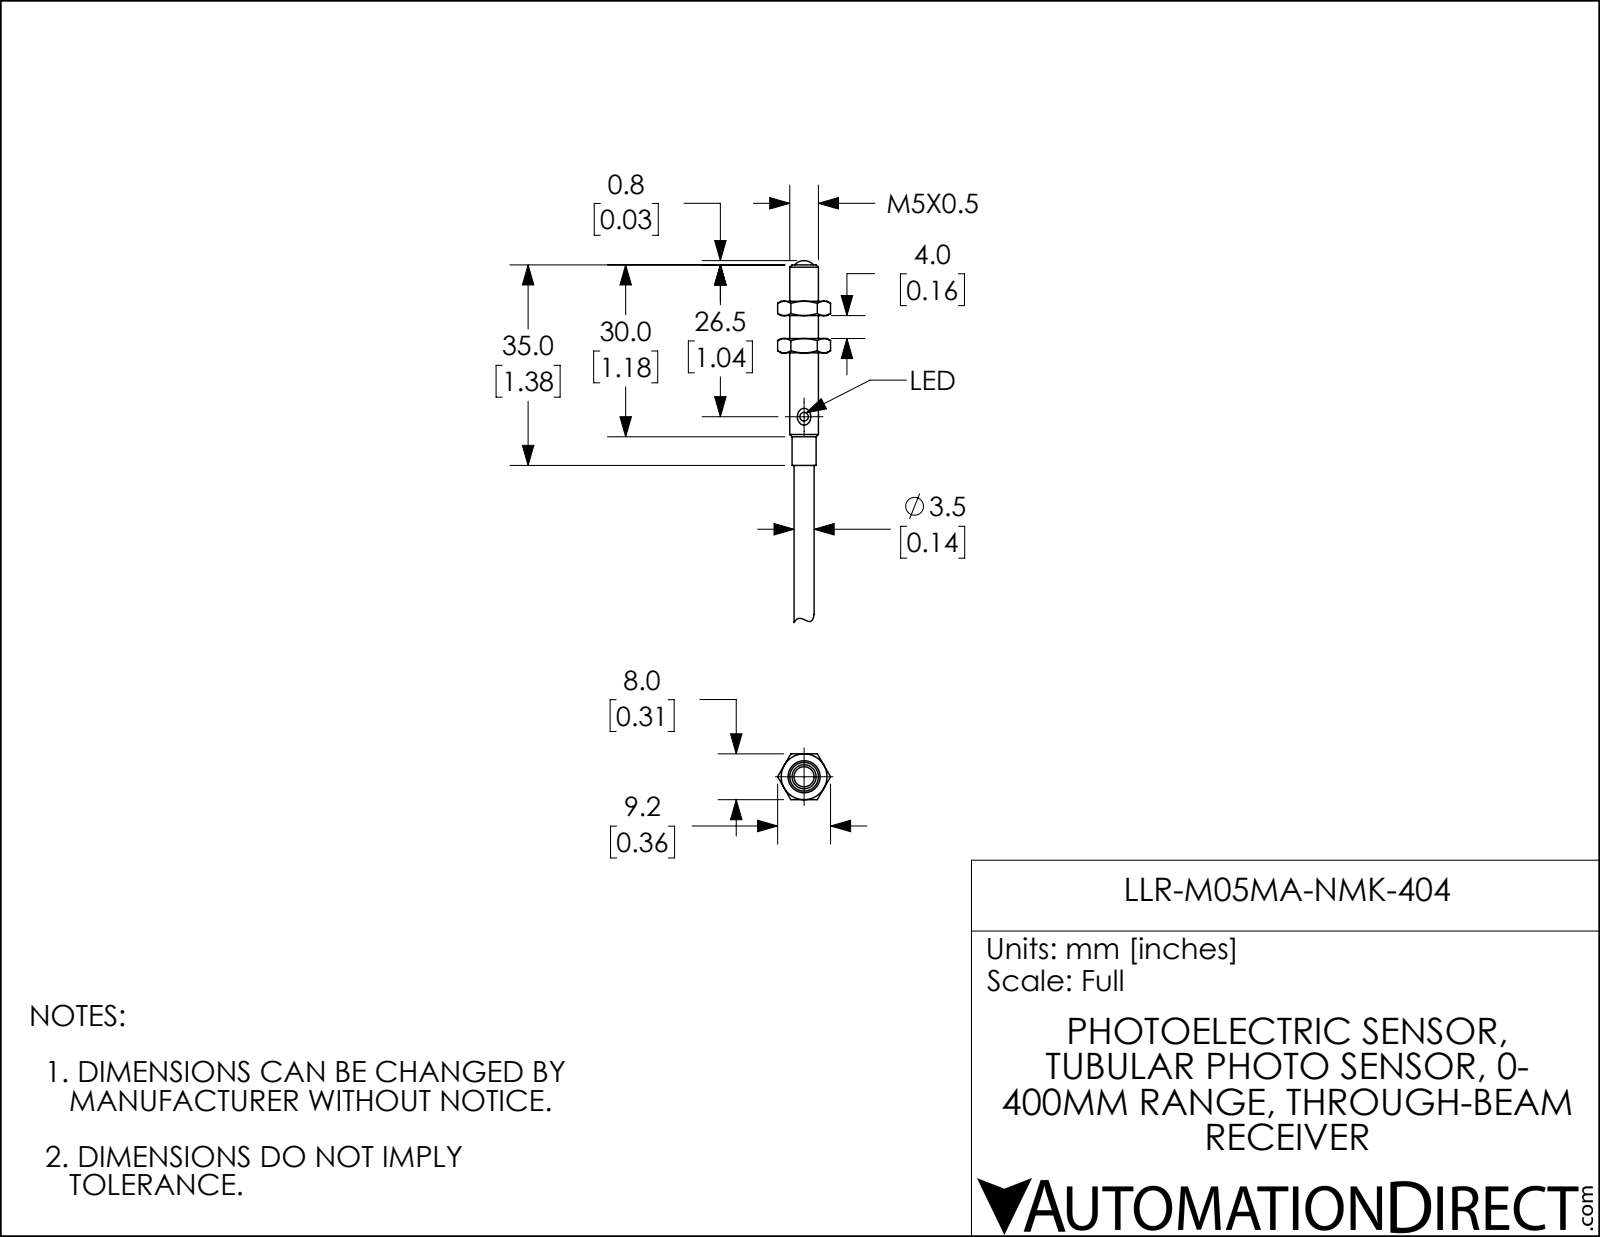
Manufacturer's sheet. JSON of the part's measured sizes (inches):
{"part_name": "LLR-M05MA-NMK-404", "step_written_by": "SolidWorks 2018 (AUTOMOTIVE_DESIGN)", "units": "inches", "bodies": {"solids": 4, "faces": 65, "planar": 21, "cylindrical": 10, "other": 34}, "overall_size": [2.487, 0.364, 0.315], "volume_in3": 0.074, "surface_area_in2": 2.117, "round_holes": [[0.059, 1], [0.197, 1]], "round_bosses_or_shafts": [[0.165, 1], [0.14, 1], [0.138, 1]], "face_to_face_distances": [0.315, 0.256, 0.098, 0.157, 0.354, 0.144, 0.045, 0.112, 0.211, 0.604]}
